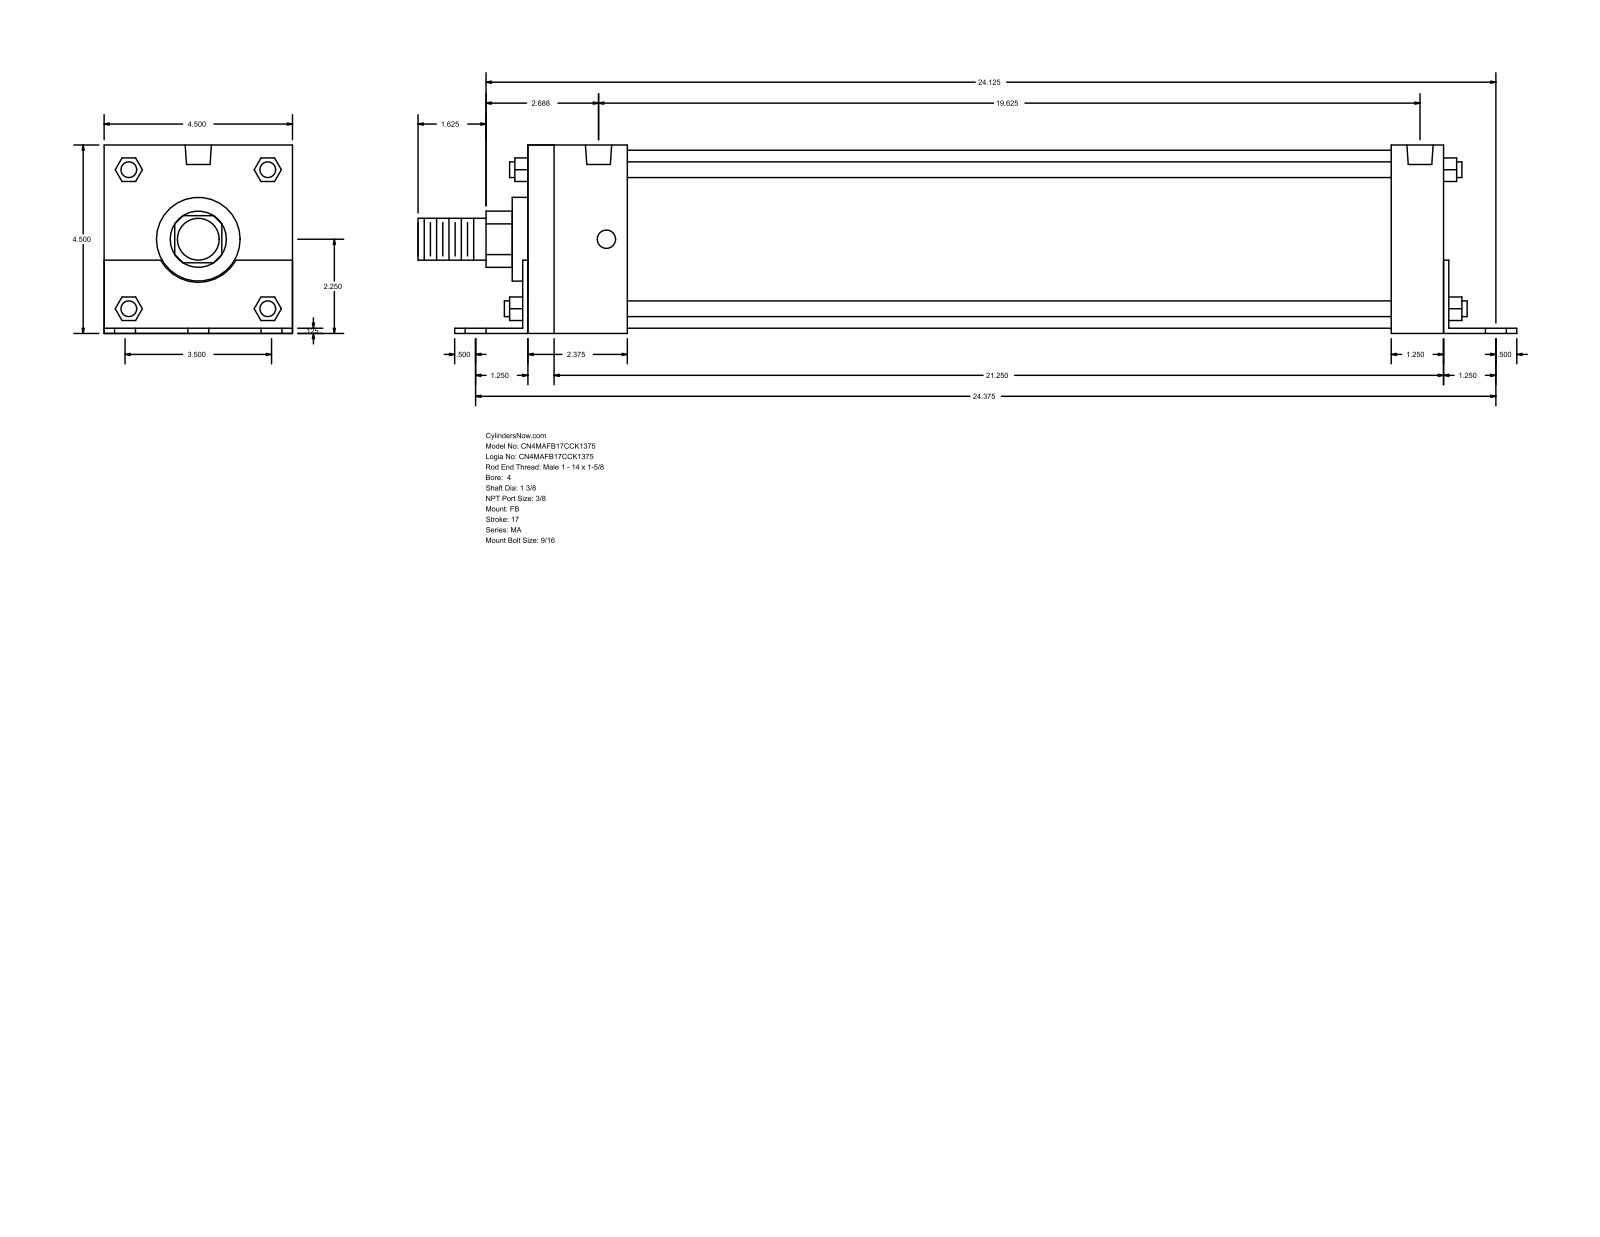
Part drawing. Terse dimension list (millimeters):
name: MA_FB__0400_1.375
written by: GSSL Pune (CONFIG_CONTROL_DESIGN)
unit: mm
bodies: 0 solids, 140 faces (105 planar, 35 cylindrical, 0 other)
size: 666.75 × 114.35 × 114.3
holes: 6× ⌀14.29, 4× ⌀11.11, 2× ⌀15.93
bosses: 4× ⌀9.53, 1× ⌀107.95, 1× ⌀50.8, 1× ⌀34.92, 1× ⌀25.4
rounds: 1× R17.06, 1× R26.16
face distances: 114.3, 3.17, 114.35, 3.12, 111.18, 555.62, 3.18, 558.8, 34.93, 558.79
hole spacings: 44.45, 620.71, 619.12, 63.99, 67.49, 86.85, 88.9, 90.98
